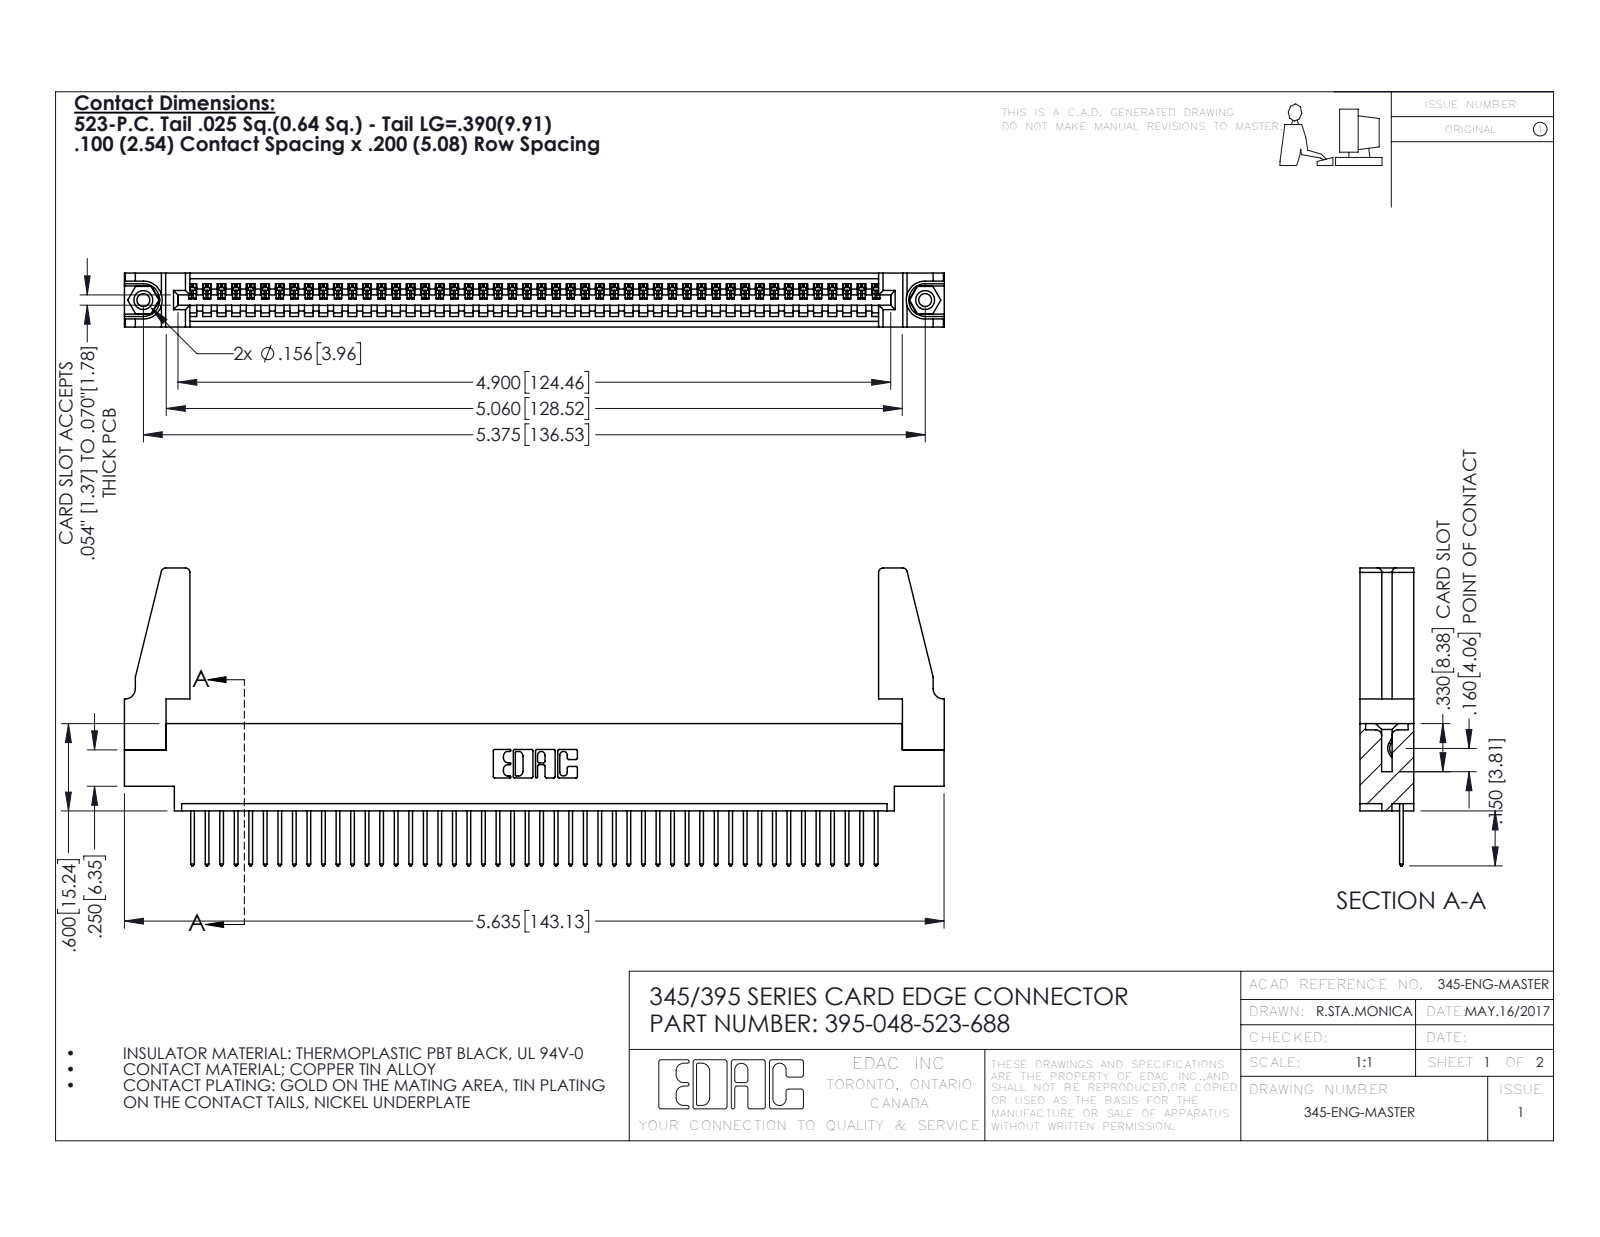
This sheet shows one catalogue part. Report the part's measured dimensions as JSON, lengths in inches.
{"part_name": "395-048-523-688; 345-292-001_345-293-123; 345-250-001_345-250-001-102; 345 Part_0.170 Offset - 0.156 Dia-TH (+1 more)", "step_written_by": "SolidWorks 2016 (CONFIG_CONTROL_DESIGN)", "units": "inches", "bodies": {"solids": 53, "faces": 3038, "planar": 2076, "cylindrical": 946, "other": 16}, "overall_size": [5.636, 2.047, 0.37], "volume_in3": 1.023, "surface_area_in2": 33.09, "round_holes": [[0.089, 2], [0.125, 2], [0.156, 2], [0.064, 1]], "round_bosses_or_shafts": [[0.155, 2]], "partial_cylinders_radius": [[0.006, 96], [0.01, 96], [0.01, 22], [0.03, 8], [0.007, 6], [0.031, 6], [0.026, 3], [0.031, 2]], "face_to_face_distances": [0.072, 0.298, 0.37, 0.098, 0.272, 0.025, 0.2, 0.225, 0.175, 0.149], "hole_center_spacings": [0.27, 5.139, 5.375]}
